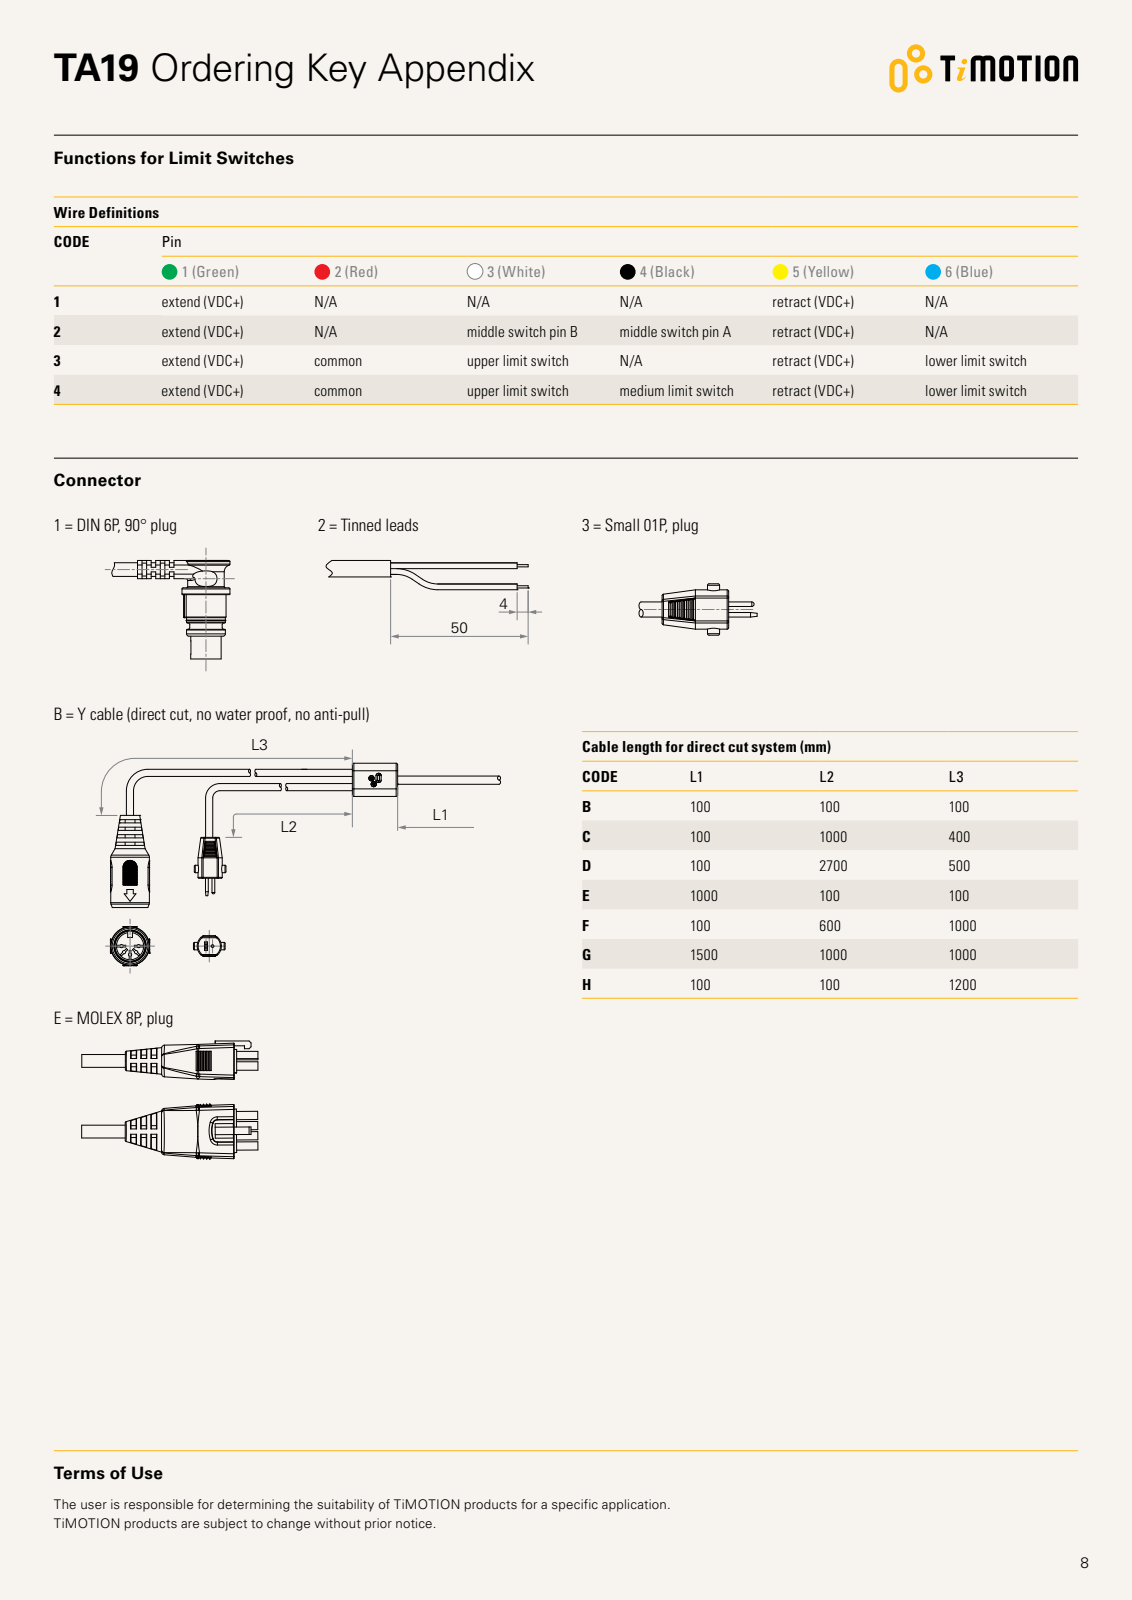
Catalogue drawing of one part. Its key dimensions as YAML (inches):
part_name: "3D_TA19 temp"
step_written_by: "SolidWorks 2010 (CONFIG_CONTROL_DESIGN)"
units: inches
bodies: {solids: 0, faces: 779, planar: 227, cylindrical: 231, other: 321}
overall_size: [15.228, 3.589, 2.664]
round_holes:
  - {diameter: 0.276, count: 6}
  - {diameter: 0.323, count: 1}
  - {diameter: 0.402, count: 1}
  - {diameter: 0.413, count: 1}
round_bosses_or_shafts:
  - {diameter: 0.209, count: 4}
  - {diameter: 0.307, count: 2}
  - {diameter: 1.26, count: 1}
  - {diameter: 1.209, count: 1}
  - {diameter: 1.063, count: 1}
  - {diameter: 0.945, count: 1}
  - {diameter: 0.197, count: 1}
partial_cylinders:
  - {radius: 0.039, count: 43}
  - {radius: 0.02, count: 24}
  - {radius: 0.079, count: 20}
  - {radius: 0.012, count: 18}
  - {radius: 0.157, count: 8}
  - {radius: 0.13, count: 4}
  - {radius: 0.053, count: 2}
  - {radius: 0.059, count: 2}
face_to_face_distances: [3.497, 1.772, 5.213, 7.642, 3.583, 12.854, 0.78, 0.992, 0.118, 1.291]
hole_center_spacings: [3.205, 0.906, 0.907, 0.933, 1.26, 1.28, 1.419, 1.52]
